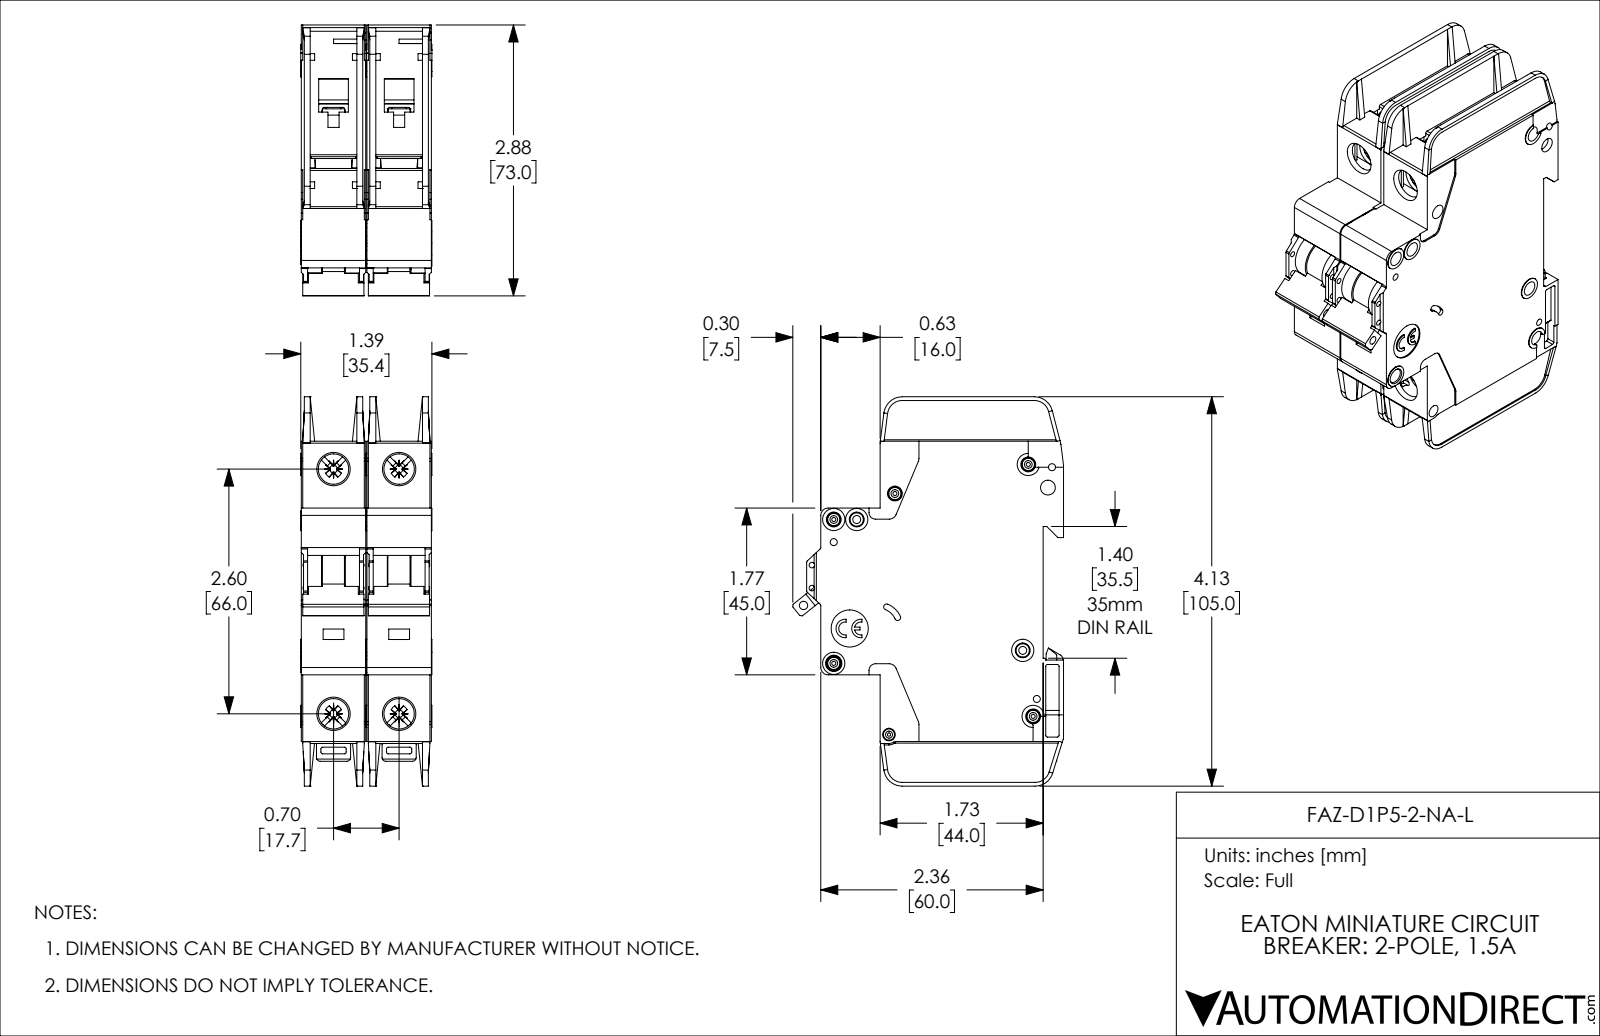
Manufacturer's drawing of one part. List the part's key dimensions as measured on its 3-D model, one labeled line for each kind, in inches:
Part name (STEP PRODUCT): FAZ-D1P5-2-NA-L
STEP written by: SolidWorks 2019 (AUTOMOTIVE_DESIGN)
Units: inches
Bodies: 2 solids, 2254 faces (1342 planar, 714 cylindrical, 198 other)
Overall size (bounding box): 4.134 × 2.876 × 1.394
Volume: 9.365 in³ · Surface area: 82.01 in²
Round holes (diameter × count): ⌀0.157 ×8, ⌀0.043 ×5, ⌀0.075 ×4, ⌀0.323 ×4, ⌀0.059 ×2, ⌀0.085 ×2, ⌀0.035 ×1, ⌀0.089 ×1, ⌀0.098 ×1, ⌀0.134 ×1, ⌀0.394 ×1
Round bosses / shafts (diameter × count): ⌀0.13 ×5, ⌀0.236 ×4, ⌀0.118 ×3, ⌀0.098 ×2
Partial cylindrical surfaces — rounded edges, fillets, slot ends (radius × count): R0.02 ×57, R0.016 ×20, R0.039 ×14, R0.079 ×10, R0.043 ×8, R0.008 ×5, R0.197 ×5, R0.01 ×4
Main face-to-face distances: 0.697, 0.047, 0.685, 0.591, 0.094, 0.638, 0.543, 1.382, 0.744, 0.65
Hole centre spacings: 0.244, 0.537, 0.697, 0.87, 2.598, 2.69, 0.189, 0.199
